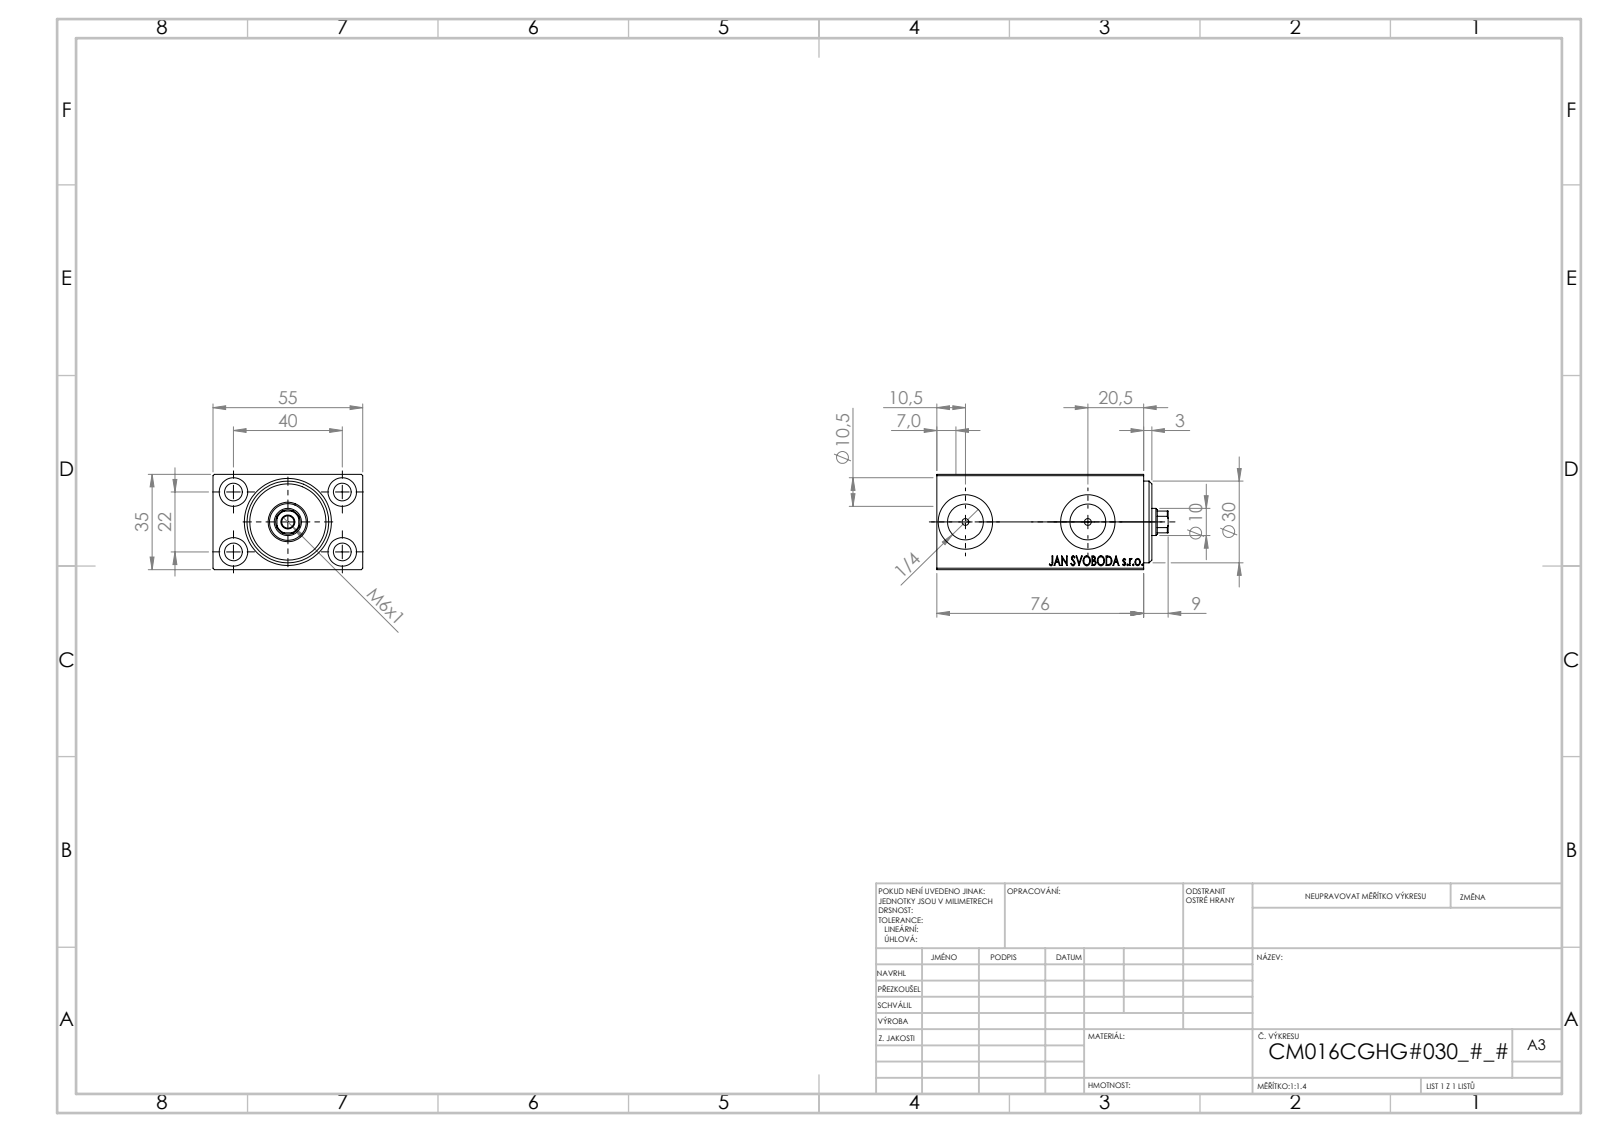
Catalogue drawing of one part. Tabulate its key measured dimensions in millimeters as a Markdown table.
| quantity | value |
| --- | --- |
| part name | V450CM_C_VCP; V450CM_C_Body; V450CM_VC_B |
| STEP written by | SolidWorks 2019 (CONFIG_CONTROL_DESIGN) |
| units | millimeters |
| bodies | 3 solids, 865 faces (409 planar, 62 cylindrical, 394 other) |
| overall size | 85 × 55 × 35 |
| volume | 127 970 mm³ |
| surface area | 35 382 mm² |
| round holes (diameter × count) | 6.5 × 4, 10.5 × 4, 2.5 × 2, 13.16 × 2, 20 × 2, 4.5 × 1, 10 × 1, 13.5 × 1, 14.5 × 1, 16 × 1, 18 × 1, 30 × 1 |
| partial cylindrical surfaces (radius × count) | 4.5 × 1 |
| main face-to-face distances | 35, 55, 71, 5, 76, 2, 8, 3, 79, 62 |
| hole center spacings | 22.83, 22, 40, 45.65, 45 |
